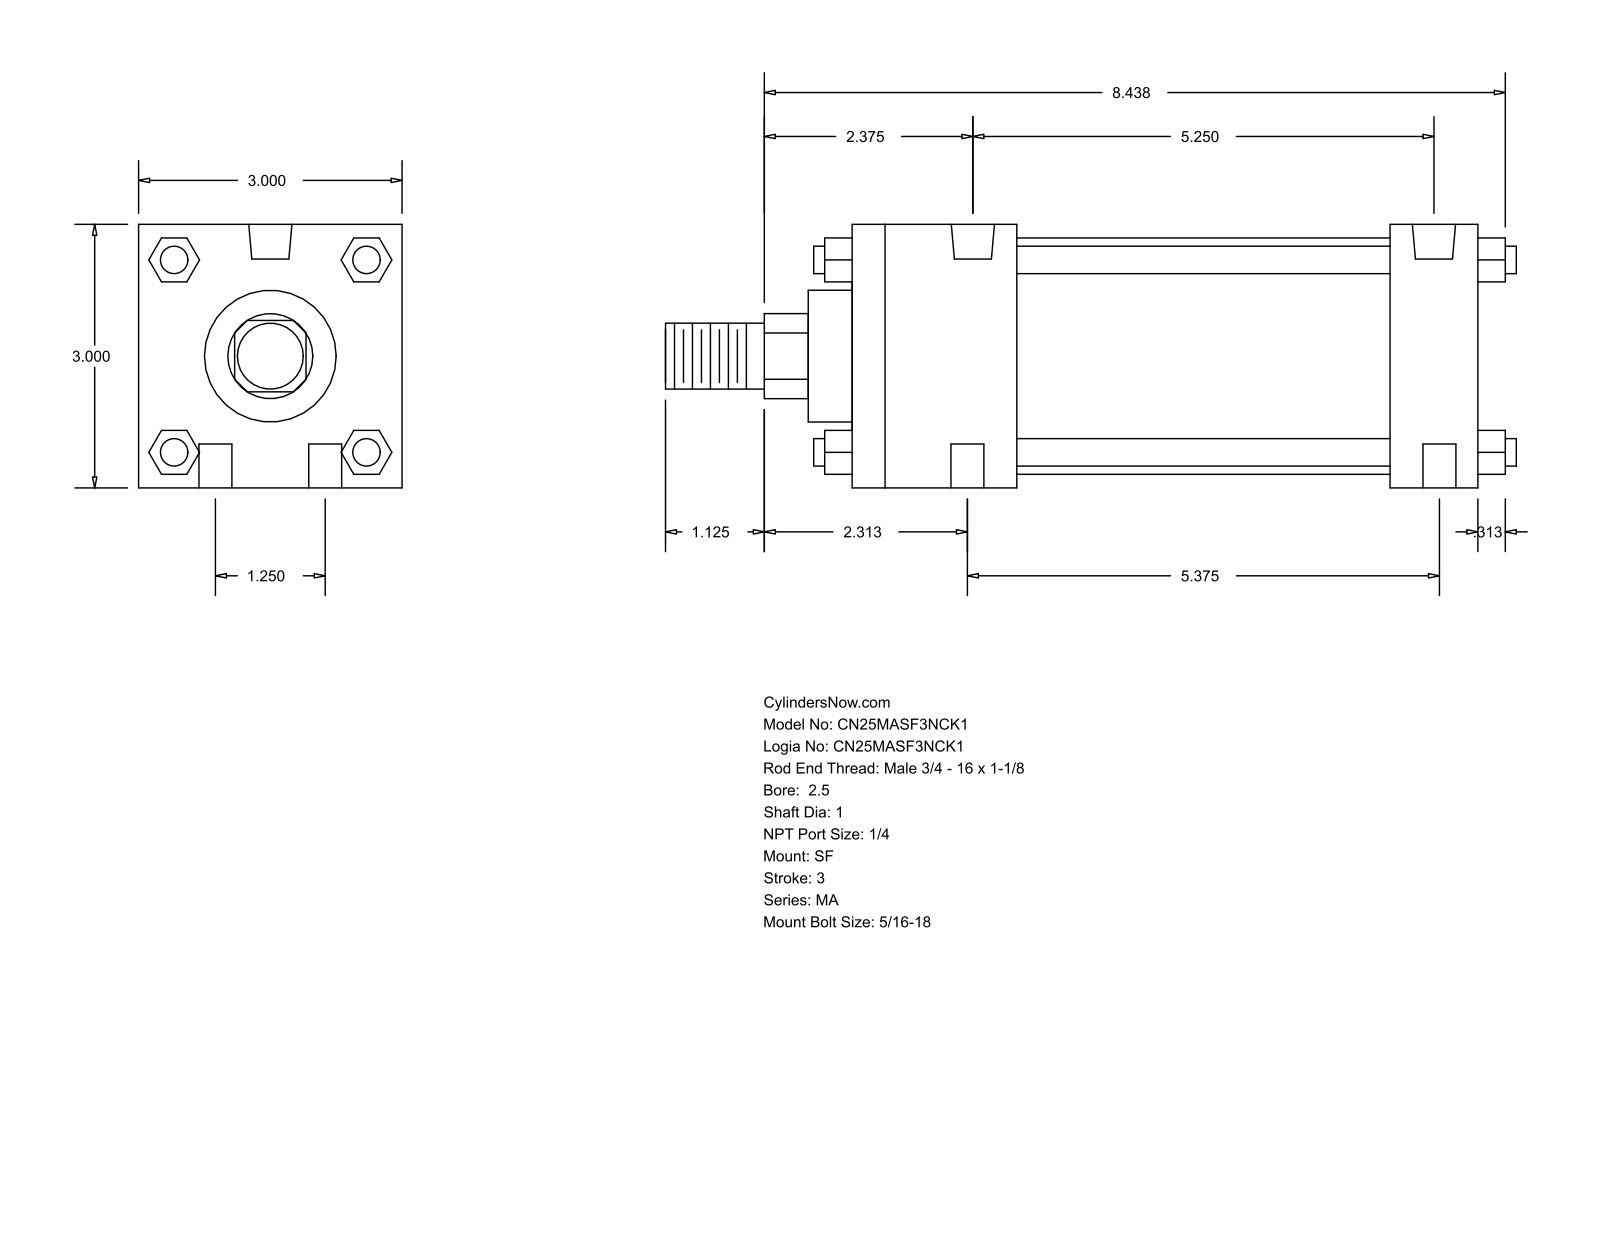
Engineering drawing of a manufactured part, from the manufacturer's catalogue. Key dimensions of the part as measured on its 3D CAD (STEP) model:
Part name (STEP PRODUCT): MA_SF__0250_1
STEP written by: GSSL Pune (CONFIG_CONTROL_DESIGN)
Units: millimetres
Bodies: 0 solids, 124 faces (94 planar, 30 cylindrical, 0 other)
Overall size (bounding box): 246.06 × 76.2 × 76.2
Round holes (diameter × count): ⌀9.53 ×4, ⌀7.94 ×2, ⌀12.49 ×2
Round bosses / shafts (diameter × count): ⌀7.94 ×4, ⌀68.33 ×1, ⌀38.1 ×1, ⌀25.4 ×1, ⌀19.05 ×1
Partial cylindrical surfaces — rounded edges, fillets, slot ends (radius × count): R12.29 ×1
Main face-to-face distances: 76.2, 180.98, 12.7, 155.57, 25.41, 47.63, 107.94, 133.35, 27.81, 48.17
Hole centre spacings: 15.96, 31.76, 133.35, 135.86, 135.87, 136.52, 140.17
